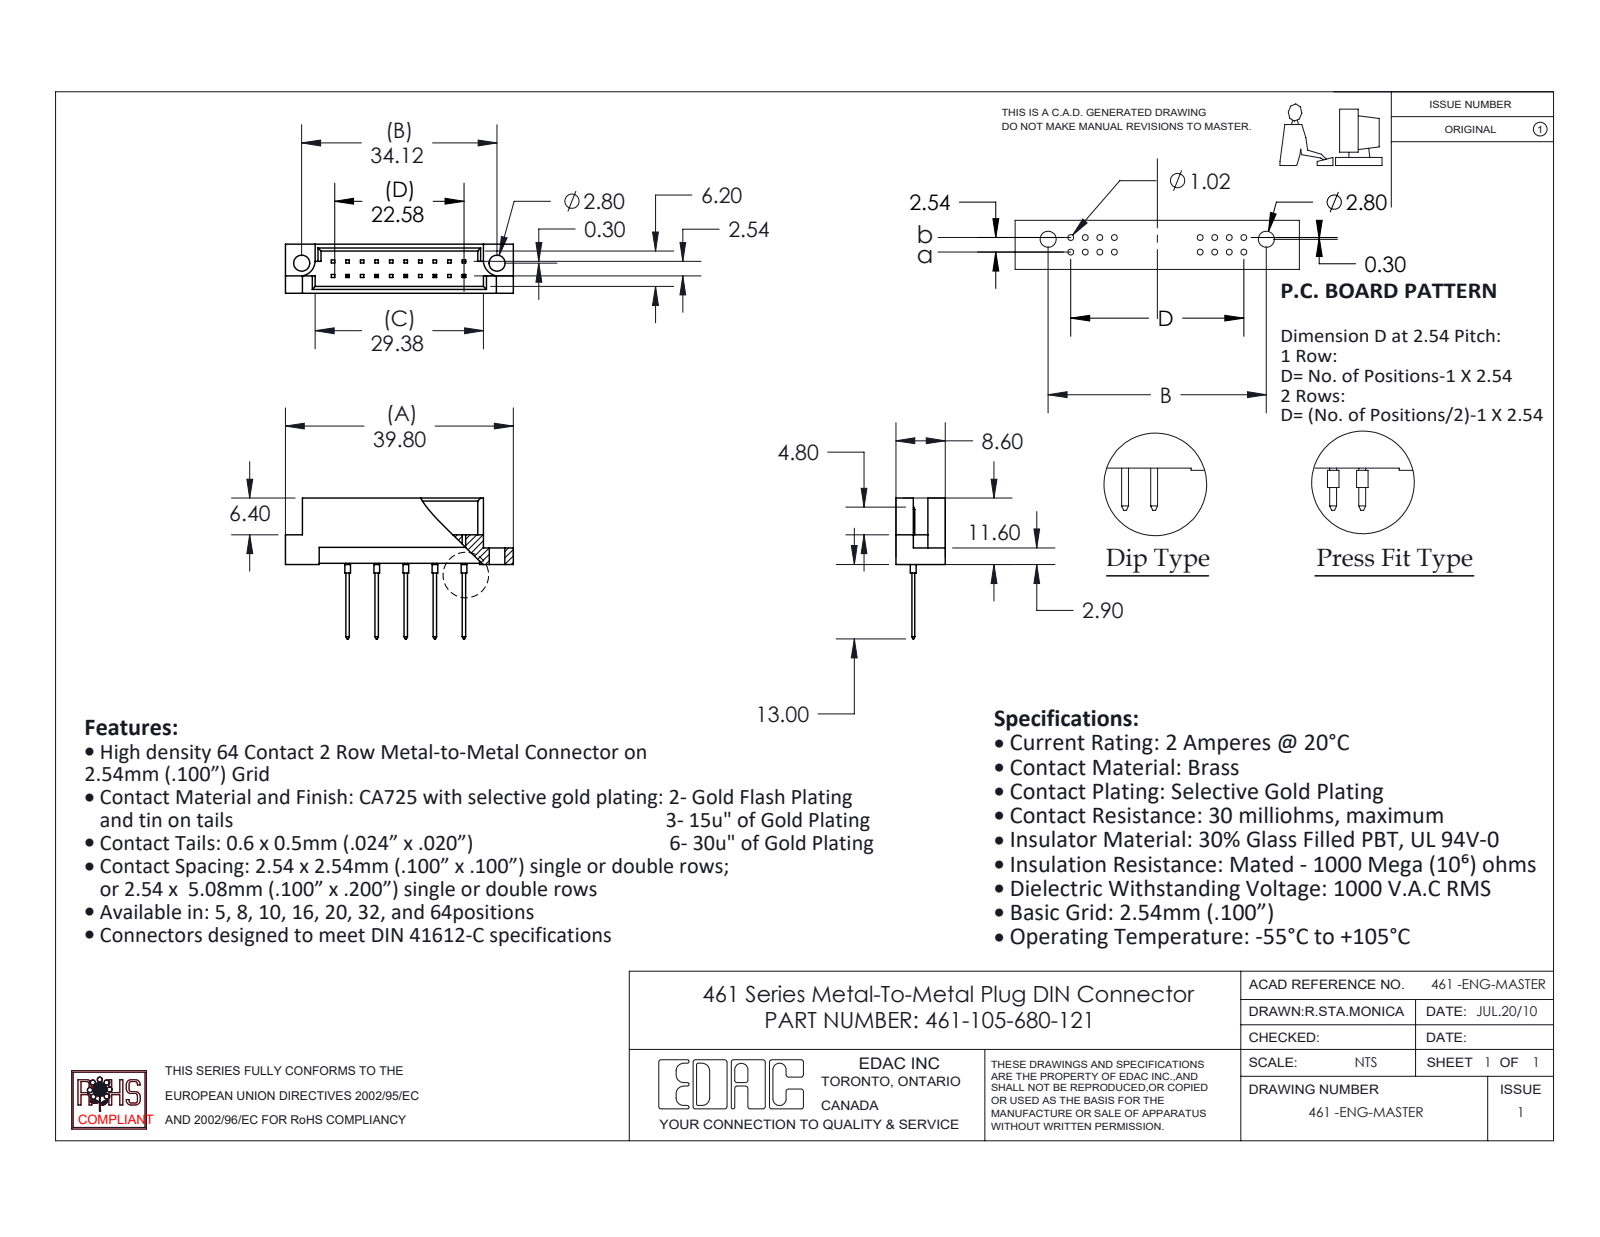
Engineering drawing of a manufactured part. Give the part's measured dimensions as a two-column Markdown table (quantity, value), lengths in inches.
| quantity | value |
| --- | --- |
| part name | 461-105-680-121; 461-290_80; 461 Part_20 |
| STEP written by | SolidWorks 2020 (CONFIG_CONTROL_DESIGN) |
| units | inches |
| bodies | 6 solids, 238 faces (222 planar, 16 cylindrical, 0 other) |
| overall size | 1.567 × 0.969 × 0.339 |
| volume | 0.119 in³ |
| surface area | 4.032 in² |
| round holes (diameter × count) | 0.11 × 2 |
| round bosses / shafts (diameter × count) | 0.039 × 5 |
| partial cylindrical surfaces (radius × count) | 0.11 × 2 |
| main face-to-face distances | 0.047, 0.291, 0.339, 0.244, 0.197, 0.2, 0.129, 0.209, 0.082, 0.162 |
| hole center spacings | 1.343 |
